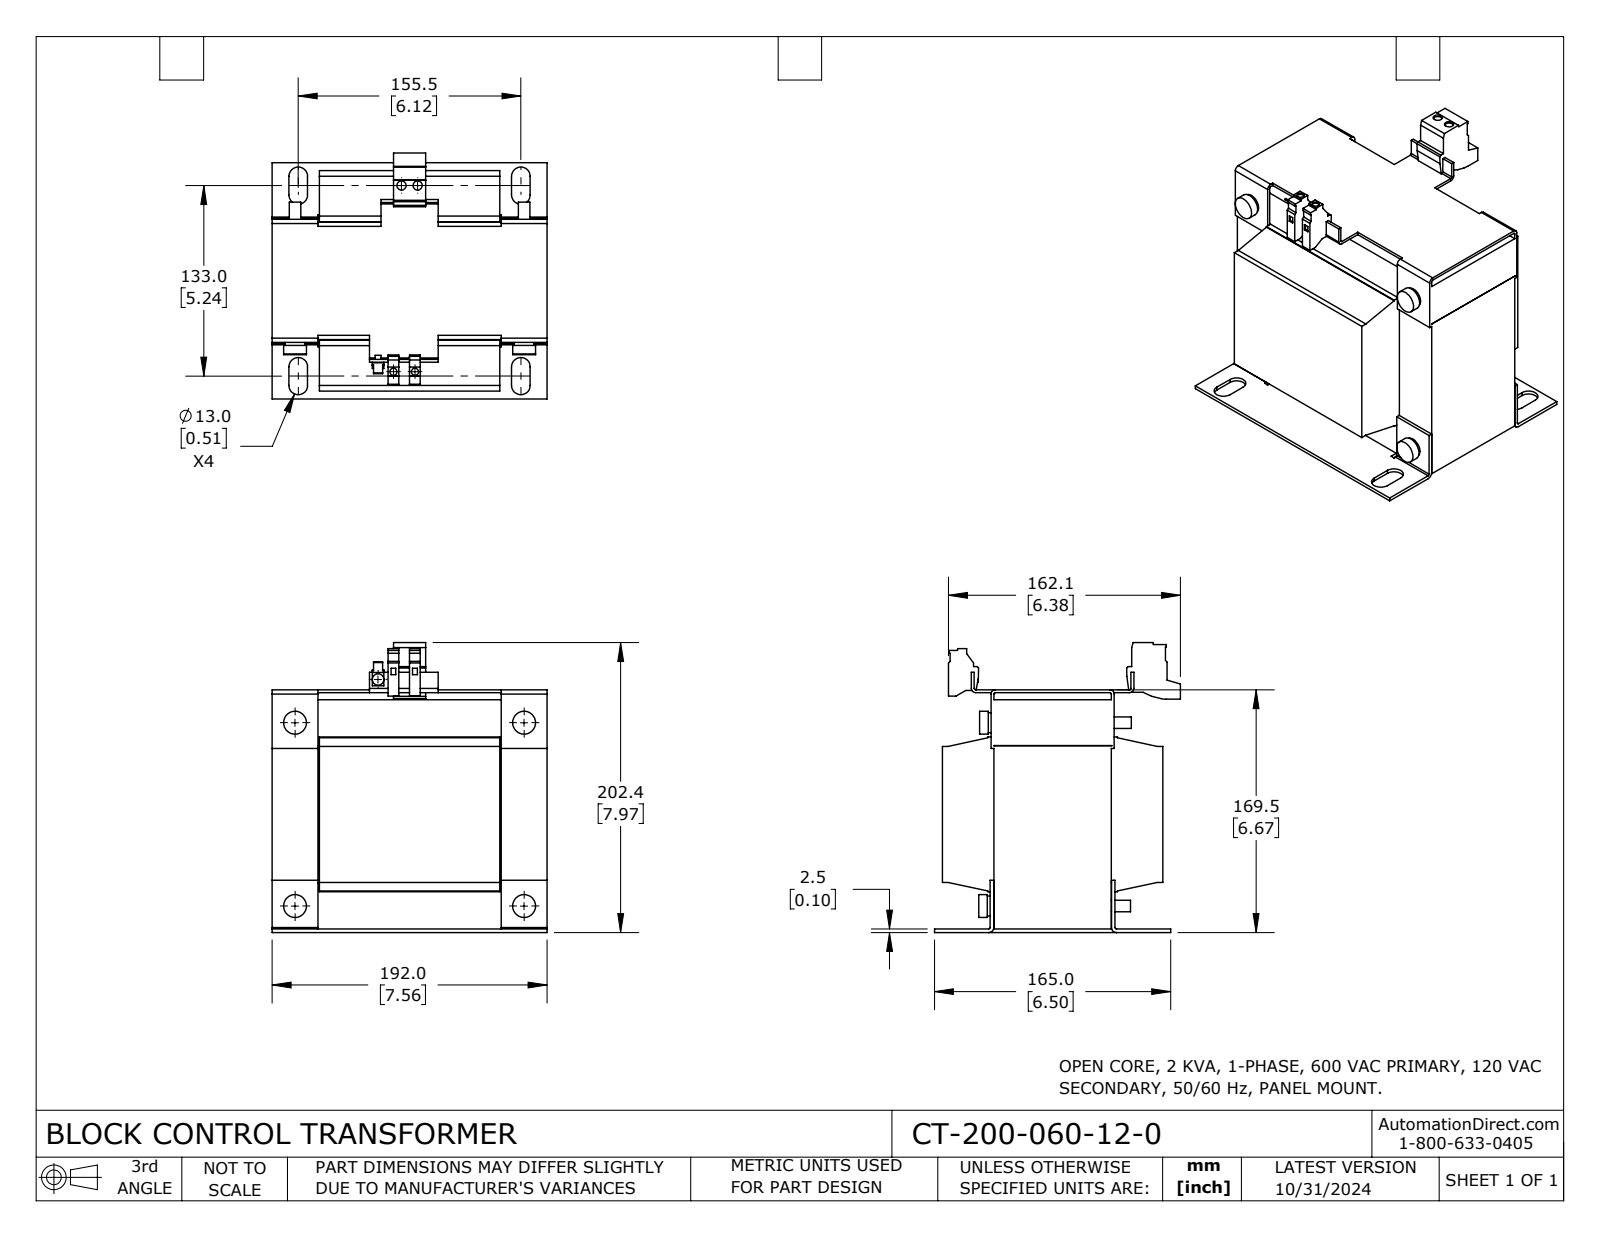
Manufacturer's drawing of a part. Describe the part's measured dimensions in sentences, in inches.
The part is named "CT-200-060-12-0". Its 3-D file was written by "SolidWorks 2023 (CONFIG_CONTROL_DESIGN)". It is 1 solid with 325 faces: 243 planar, 82 cylindrical and 0 other. Overall it measures 7.969 by 7.559 by 6.764 inches. Its volume is 218 cubic inches and its surface area 494.9 square inches. Round holes: 2 of diameter 0.197, 2 of diameter 0.252. Round bosses or shafts: 5 of diameter 0.315, 4 of diameter 0.63, 4 of diameter 0.551, 2 of diameter 0.394, 1 of diameter 0.157. Partial cylindrical surfaces (rounded edges, fillets, slot ends): 8 of radius 0.256, 6 of radius 0.039, 4 of radius 0.118, 2 of radius 0.138, 1 of radius 0.591. The main face-to-face distances are 1.26, 5.039, 6.299, 1.299, 6.26, 5.138, 1.417, 4.646, 0.098, 0.079. The hole center spacings are 0.443, 0.591, 5.119, 5.123, 5.131, 5.161.
